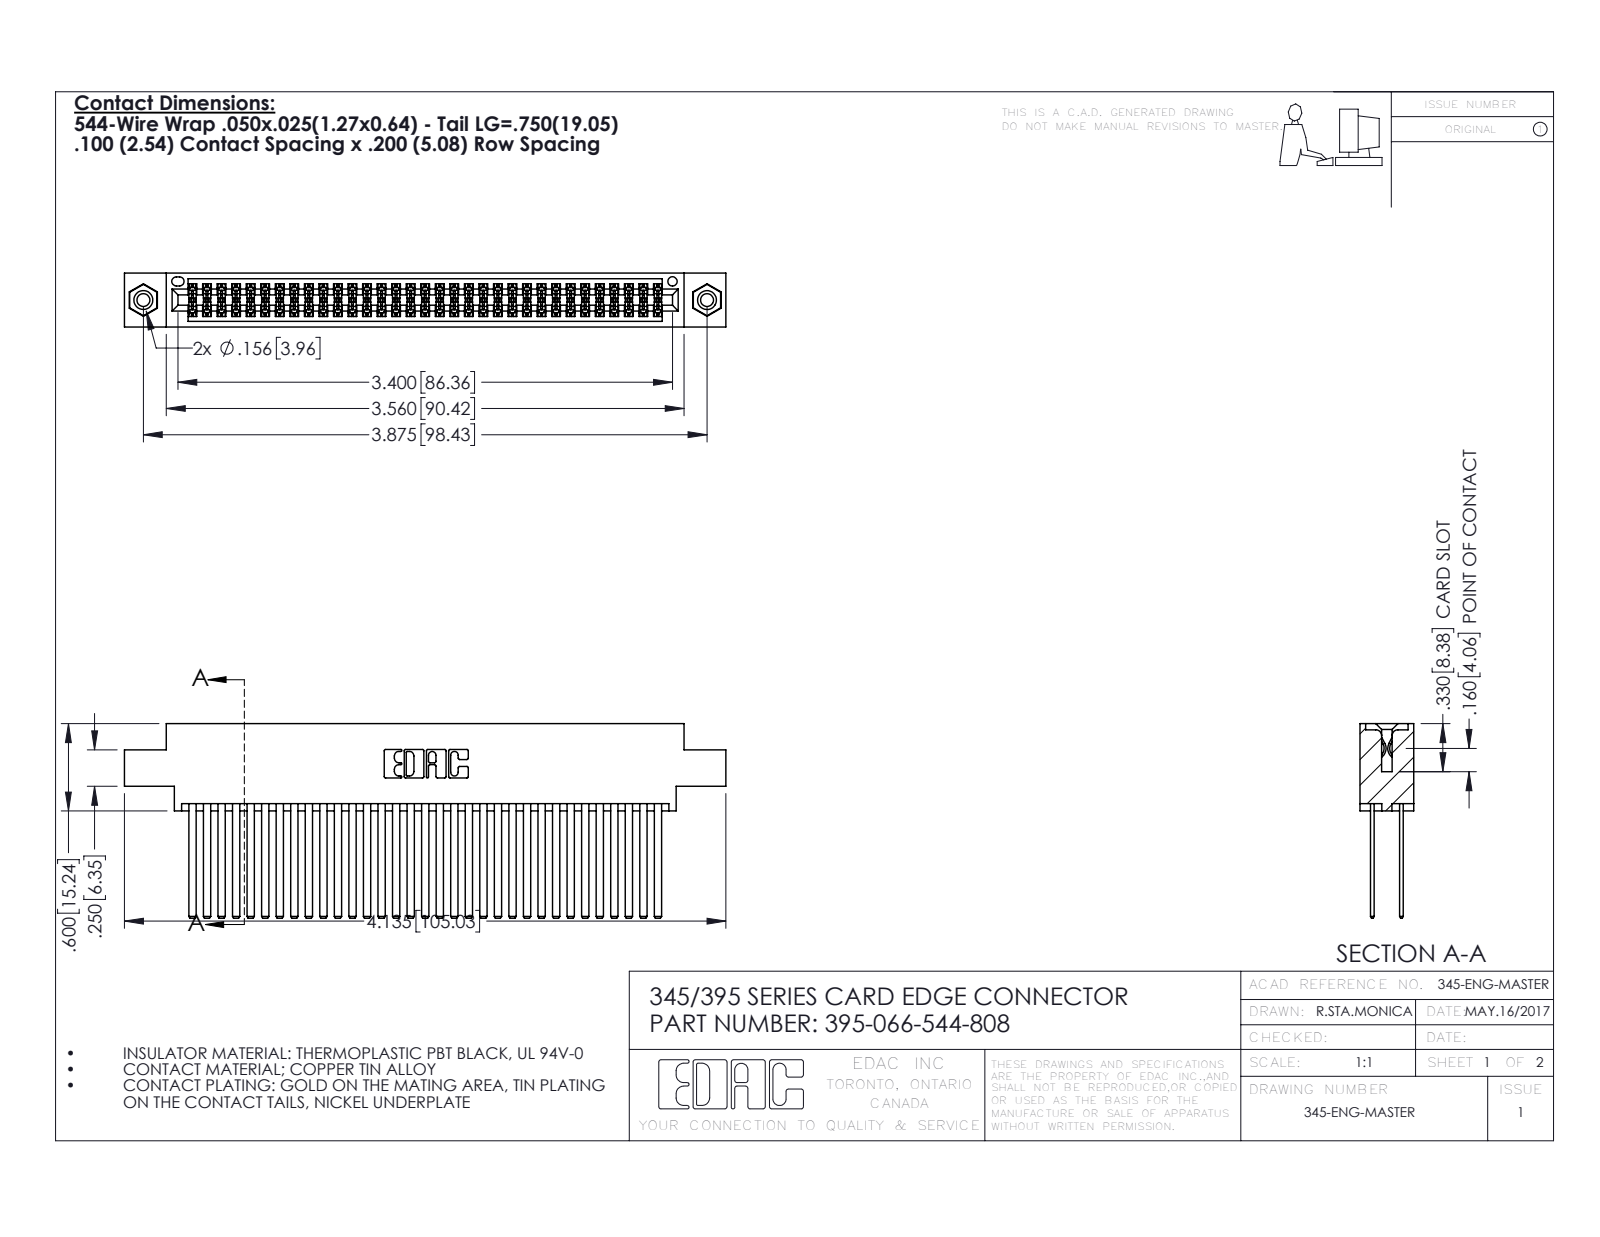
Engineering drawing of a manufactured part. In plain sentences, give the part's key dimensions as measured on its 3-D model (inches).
The part is named "345 Part_0.170 Offset - 0.156 Dia-TI; 345-292-001_345-293-144; 345-250-001_345-250-003-102; 395-066-544-808". Its 3-D file was written by "SolidWorks 2016 (CONFIG_CONTROL_DESIGN)". It is 69 solids with 3094 faces: 2030 planar, 1048 cylindrical and 16 other. Overall it measures 4.135 by 1.337 by 0.37 inches. Its volume is 0.667 cubic inches and its surface area 29.21 square inches. Round holes: 2 of diameter 0.089, 2 of diameter 0.125, 2 of diameter 0.156, 1 of diameter 0.064. Round bosses or shafts: 2 of diameter 0.155. Partial cylindrical surfaces (rounded edges, fillets, slot ends): 99 of radius 0.006, 22 of radius 0.01, 6 of radius 0.007, 6 of radius 0.031, 3 of radius 0.026, 2 of radius 0.014, 2 of radius 0.019, 2 of radius 0.022. The main face-to-face distances are 0.2, 0.025, 0.072, 0.098, 0.272, 0.298, 0.225, 0.175, 0.37, 0.15. The hole center spacings are 0.27, 3.64, 3.875.
